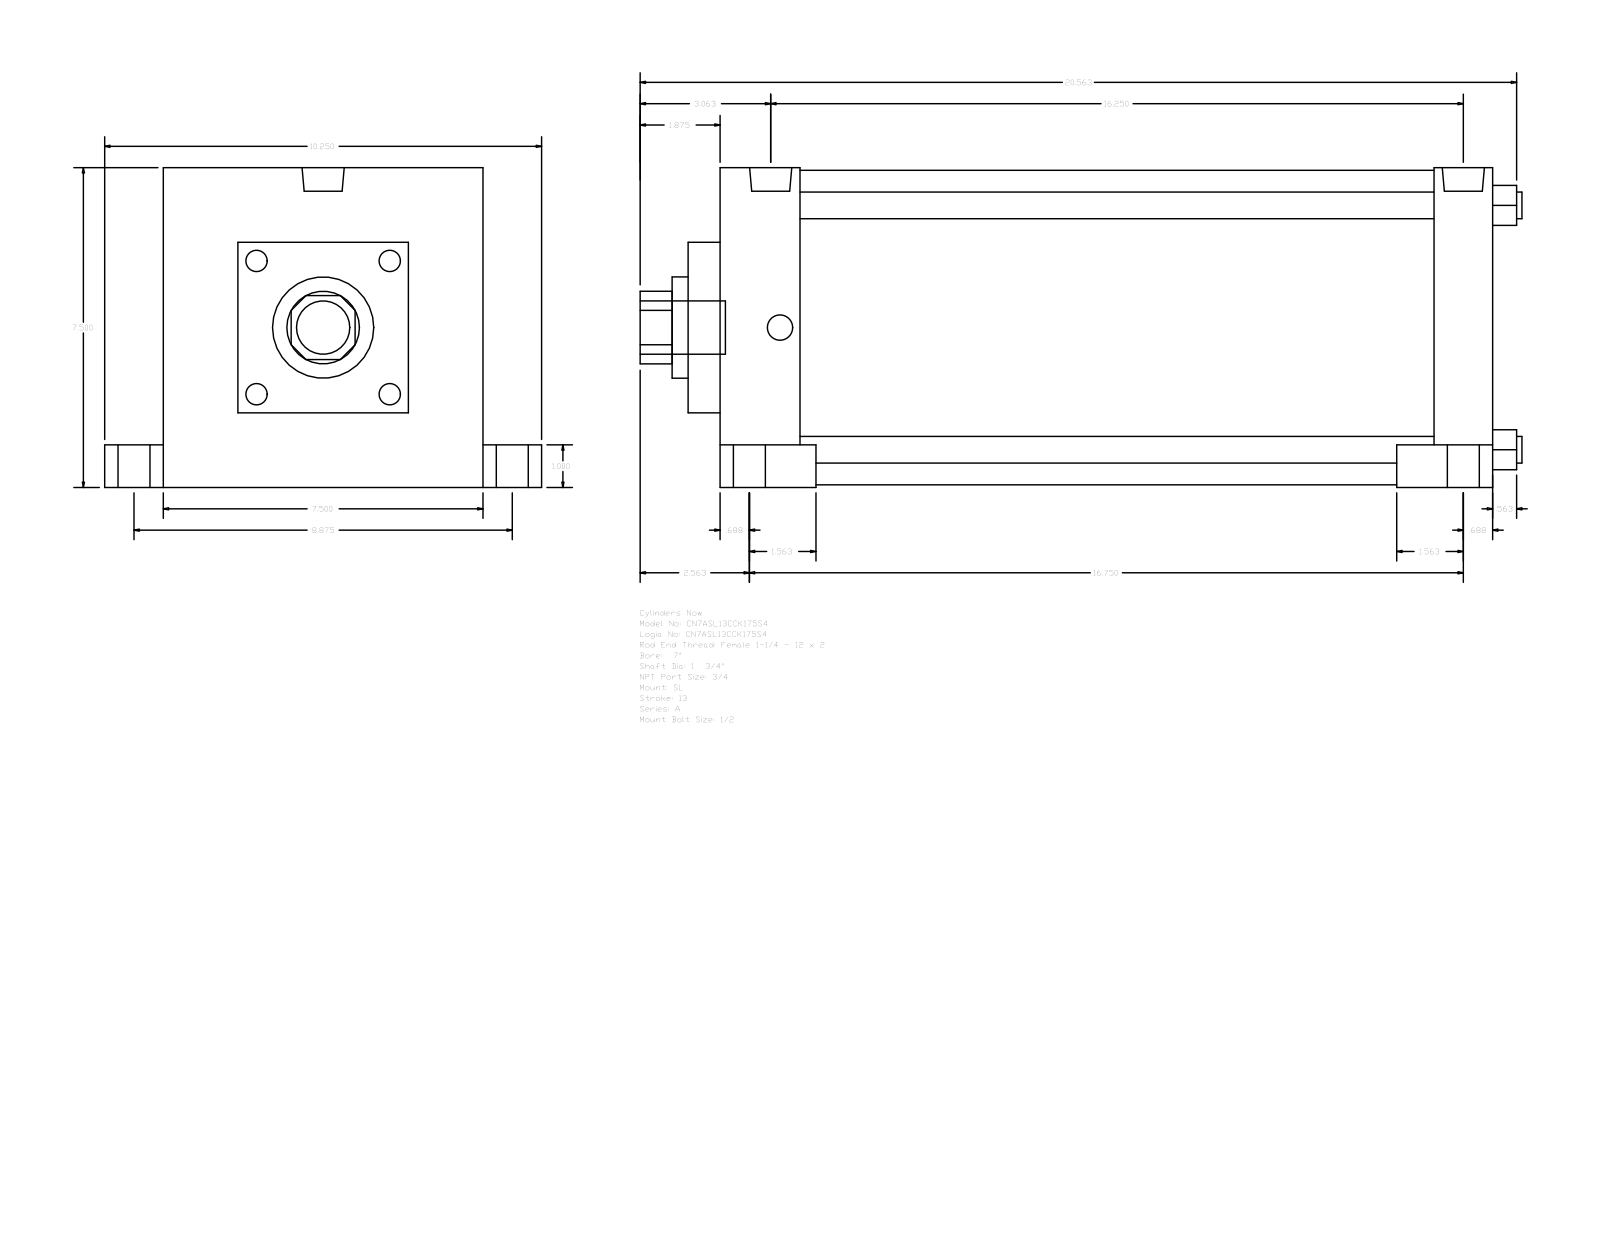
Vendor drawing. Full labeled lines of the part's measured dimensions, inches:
Part name (STEP PRODUCT): A_SL__0700_1.75
STEP written by: GSSL Pune (CONFIG_CONTROL_DESIGN)
Units: inches
Bodies: 0 solids, 117 faces (85 planar, 32 cylindrical, 0 other)
Overall size (bounding box): 20.687 × 10.25 × 7.5
Round holes (diameter × count): ⌀0.625 ×4, ⌀1.75 ×1, ⌀2.375 ×1, ⌀7.375 ×1
Round bosses / shafts (diameter × count): ⌀1 ×4, ⌀0.75 ×4, ⌀0.594 ×4, ⌀0.989 ×2, ⌀1.25 ×1
Partial cylindrical surfaces — rounded edges, fillets, slot ends (radius × count): R0.852 ×1
Main face-to-face distances: 7.5, 18.125, 1.375, 0.75, 1.75, 1.875, 16.25, 16.75, 14.875, 5.75
Hole centre spacings: 4.052, 5.73, 8.103
